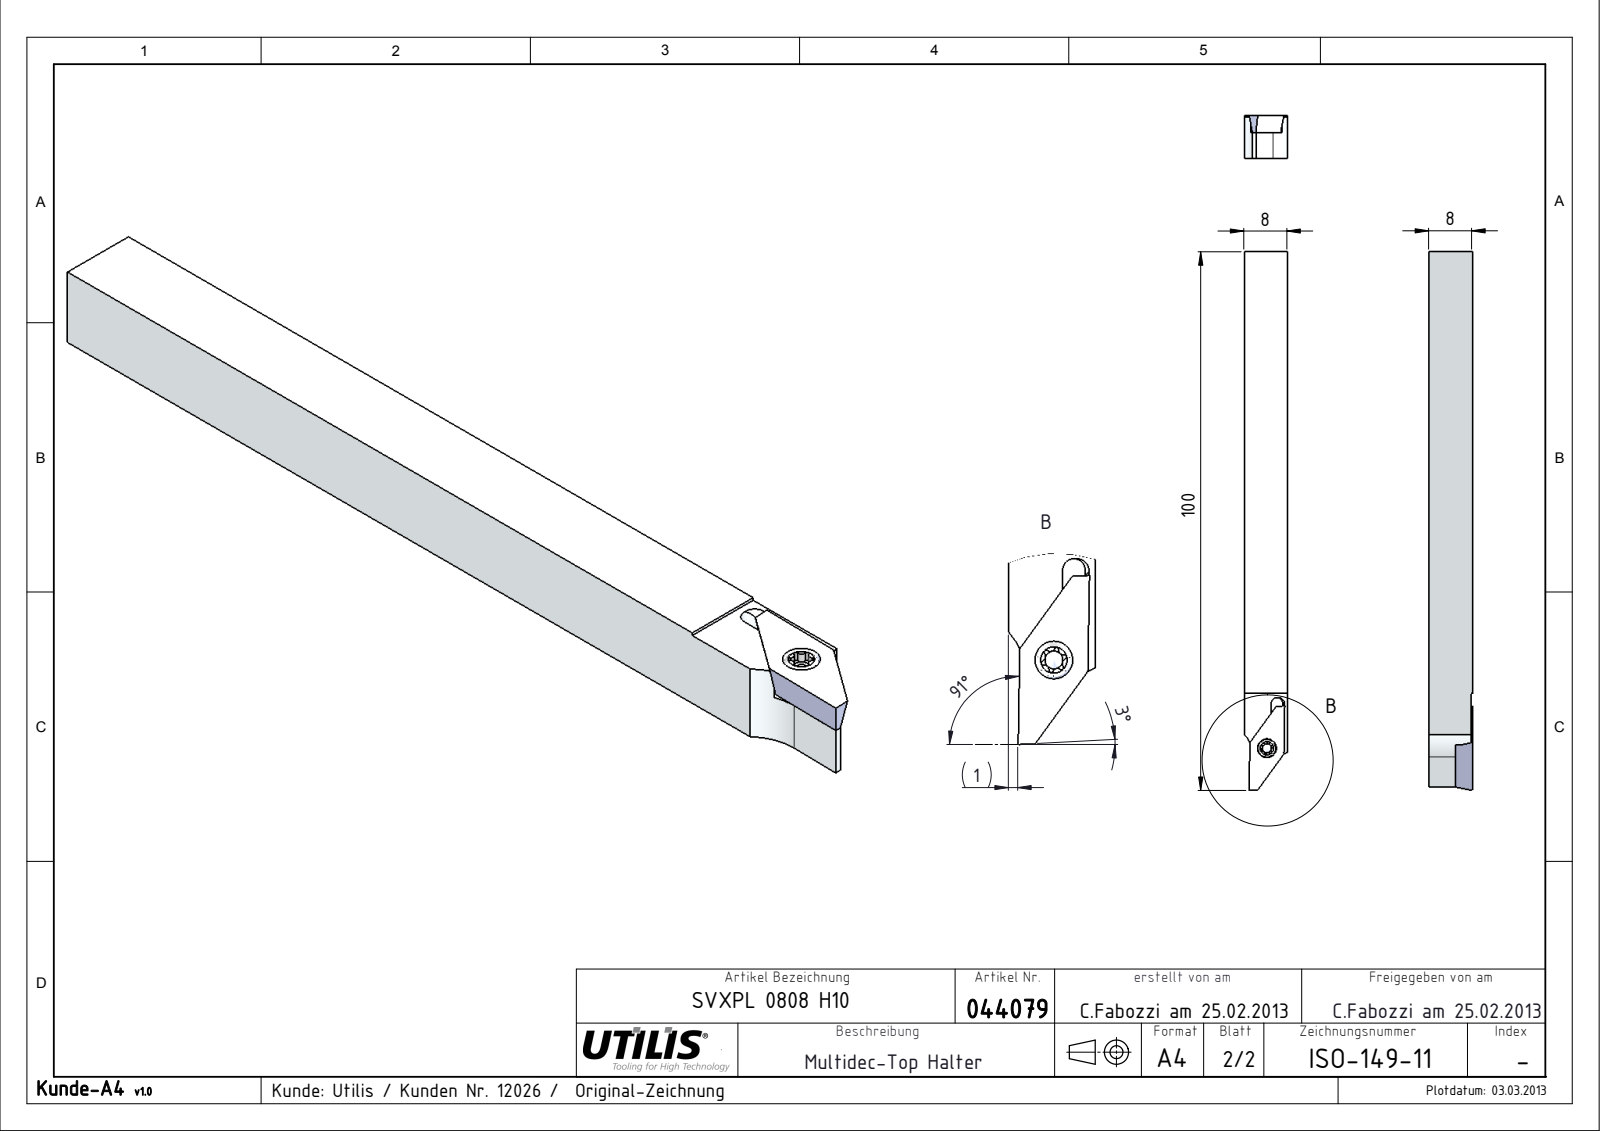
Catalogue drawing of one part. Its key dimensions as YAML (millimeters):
part_name: "ISO-149-11; VPGT 10 L_01; MSP-7_M2,5X6-TX8 CERATIZIT Schraube; ISO-149-Kunde_11"
step_written_by: "SolidWorks 2015 (CONFIG_CONTROL_DESIGN)"
units: millimeters
bodies: {solids: 3, faces: 71, planar: 27, cylindrical: 27, other: 17}
overall_size: [100, 8, 8]
volume: 6050
surface_area: 3535
round_holes:
  - {diameter: 2.05, count: 1}
  - {diameter: 3, count: 1}
round_bosses_or_shafts:
  - {diameter: 3.45, count: 1}
  - {diameter: 2.5, count: 1}
partial_cylinders:
  - {radius: 0.2, count: 6}
  - {radius: 0.45, count: 6}
  - {radius: 6, count: 2}
  - {radius: 1.05, count: 1}
face_to_face_distances: [8, 4.82, 3.18, 7.7, 2.88, 5.33, 2.1, 3.23, 5.32, 2]
